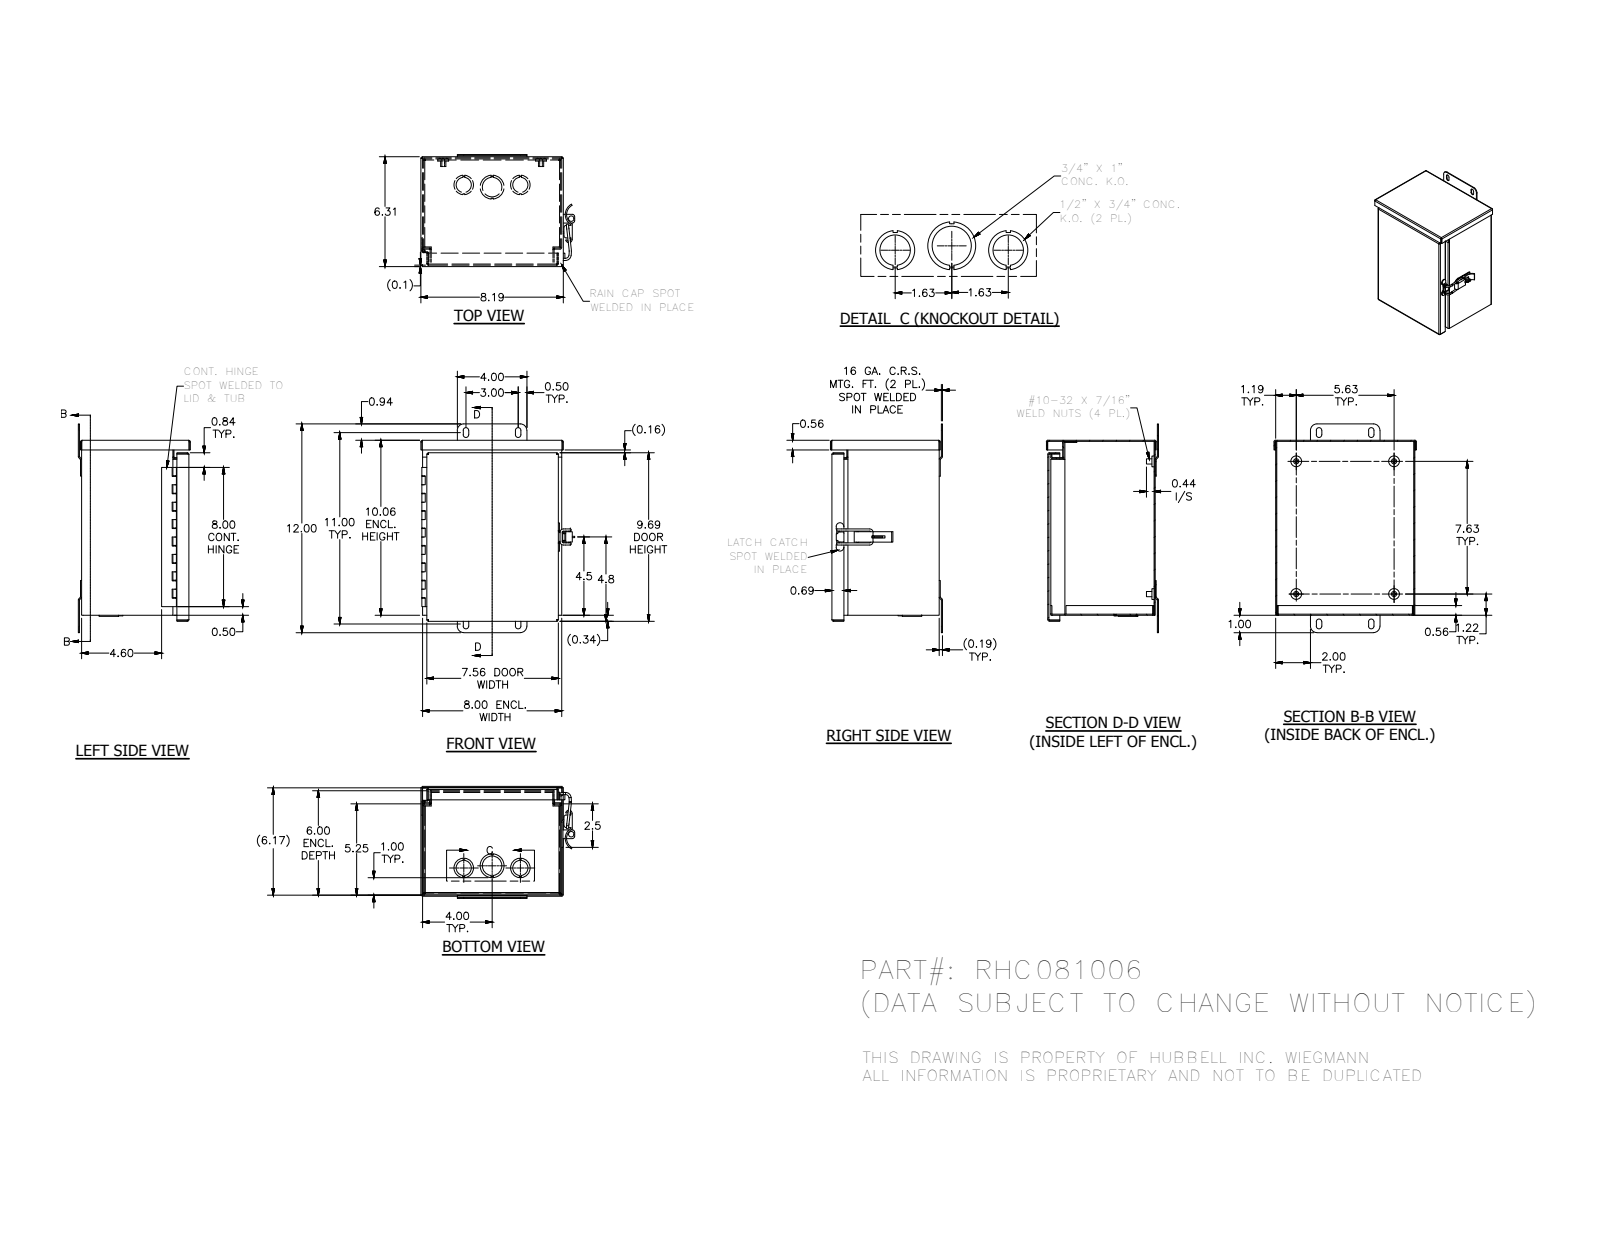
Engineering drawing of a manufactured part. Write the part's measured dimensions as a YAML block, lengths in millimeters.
part_name: "RCH08106BKPA; RHC86EWPA; RHC86CPA; RHC08ABOVEDRPA (+8 more)"
step_written_by: "Autodesk Inventor 2014 (AUTOMOTIVE_DESIGN)"
units: millimeters
bodies: {solids: 21, faces: 605, planar: 394, cylindrical: 171, other: 40}
overall_size: [304.8, 224.63, 163.58]
round_holes:
  - {diameter: 3.96, count: 4}
  - {diameter: 28.57, count: 3}
  - {diameter: 22.22, count: 2}
  - {diameter: 2.96, count: 1}
  - {diameter: 3.3, count: 1}
  - {diameter: 8, count: 1}
  - {diameter: 34.92, count: 1}
round_bosses_or_shafts:
  - {diameter: 3.17, count: 8}
  - {diameter: 15.88, count: 4}
  - {diameter: 7.62, count: 4}
  - {diameter: 5.08, count: 1}
  - {diameter: 2.54, count: 1}
partial_cylinders:
  - {radius: 0.79, count: 21}
  - {radius: 2.38, count: 21}
  - {radius: 1.59, count: 8}
  - {radius: 2.39, count: 8}
  - {radius: 3.97, count: 8}
  - {radius: 3.17, count: 6}
  - {radius: 9.53, count: 4}
  - {radius: 0.79, count: 3}
face_to_face_distances: [1.59, 155.09, 201.61, 254, 156.68, 153.5, 200.02, 203.2, 252.41, 255.59]
hole_center_spacings: [142.88, 193.67, 240.67, 15.65, 41.39, 41.4, 82.55, 89.11]
